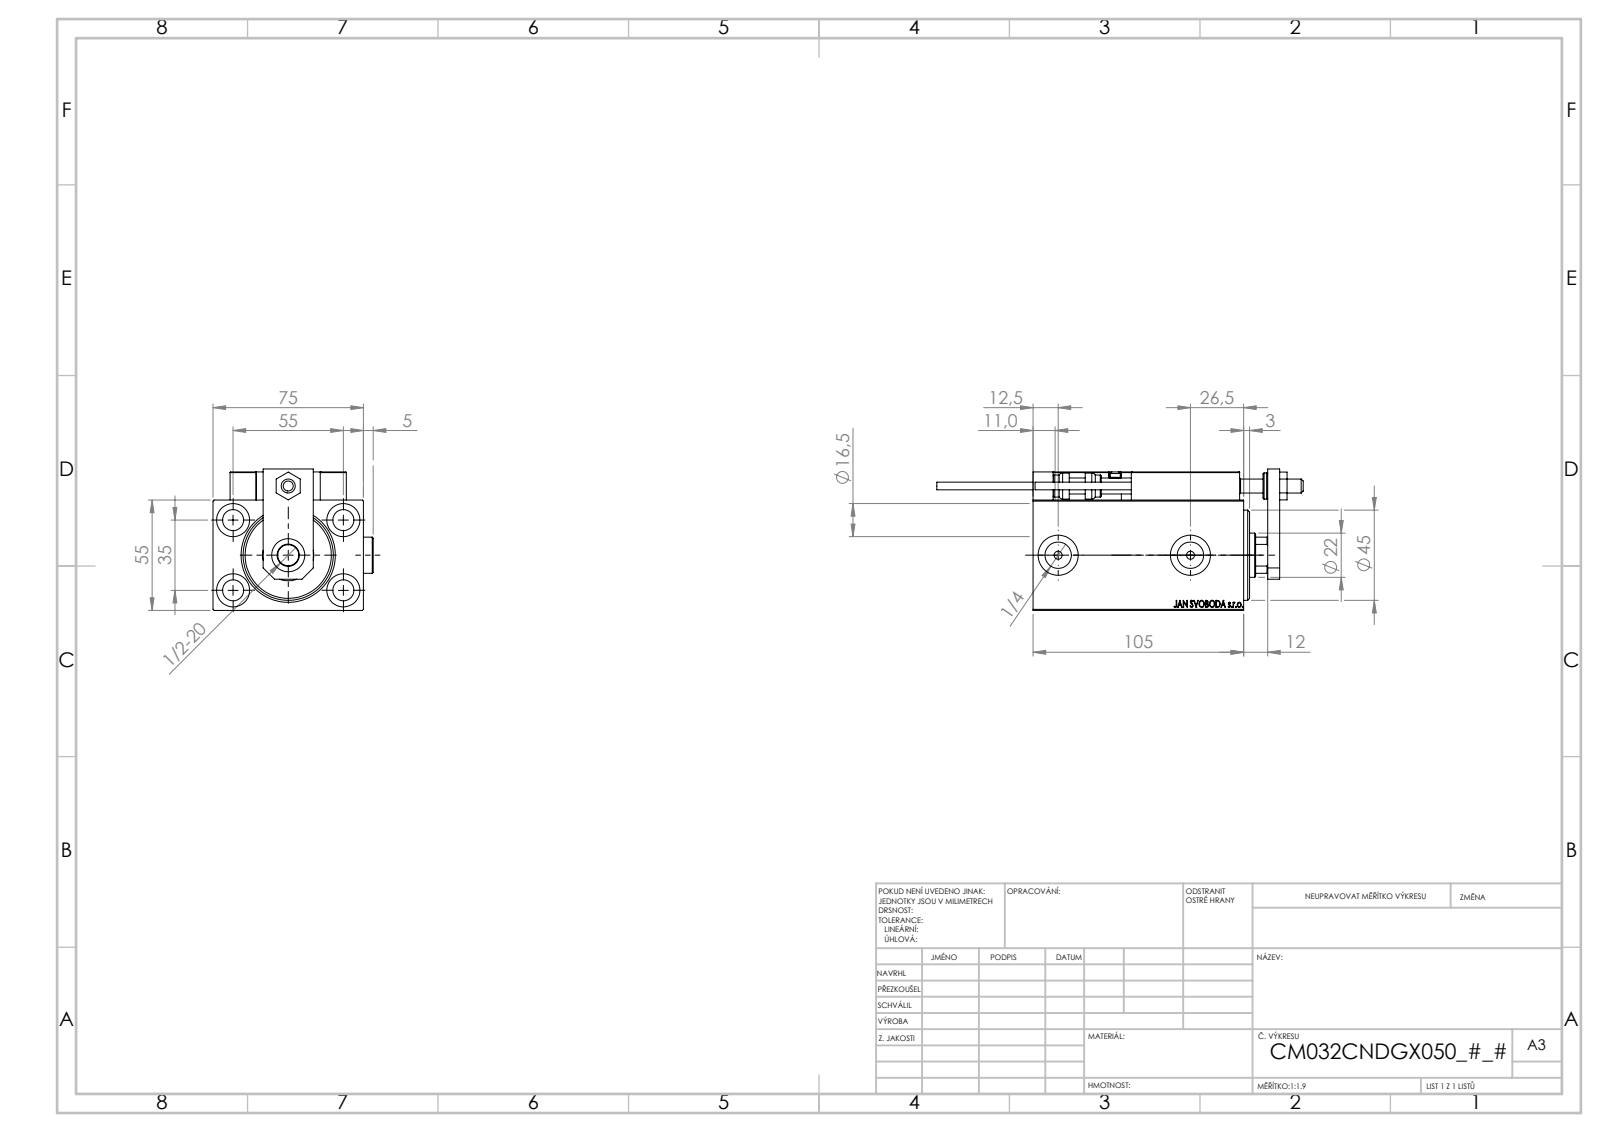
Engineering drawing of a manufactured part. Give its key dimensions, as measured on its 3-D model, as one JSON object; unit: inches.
{"part_name": "ALLEN BOLT D5; MAGNET; SWITCH DIM B,W; ALLEN BOLT D8 (+8 more)", "step_written_by": "SolidWorks 2019 (CONFIG_CONTROL_DESIGN)", "units": "inches", "bodies": {"solids": 25, "faces": 1336, "planar": 594, "cylindrical": 204, "other": 538}, "overall_size": [7.193, 3.146, 2.776], "volume_in3": 25.25, "surface_area_in2": 162.7, "round_holes": [[0.157, 6], [0.315, 5], [0.413, 5], [0.65, 5], [0.126, 4], [0.197, 2], [0.518, 2], [0.787, 2], [0.276, 1], [0.866, 1], [1.004, 1], [1.26, 1]], "round_bosses_or_shafts": [[0.709, 2], [0.197, 2], [0.15, 2], [0.512, 1], [0.433, 1]], "partial_cylinders_radius": [[0.012, 30], [0.118, 2], [0.413, 1]], "face_to_face_distances": [2.165, 2.953, 0.551, 0.394, 0.472, 0.197, 2.717, 0.276, 0.591, 0.984], "hole_center_spacings": [1.283, 0.448, 0.787, 1.165, 1.169, 1.273, 1.378, 1.42]}
